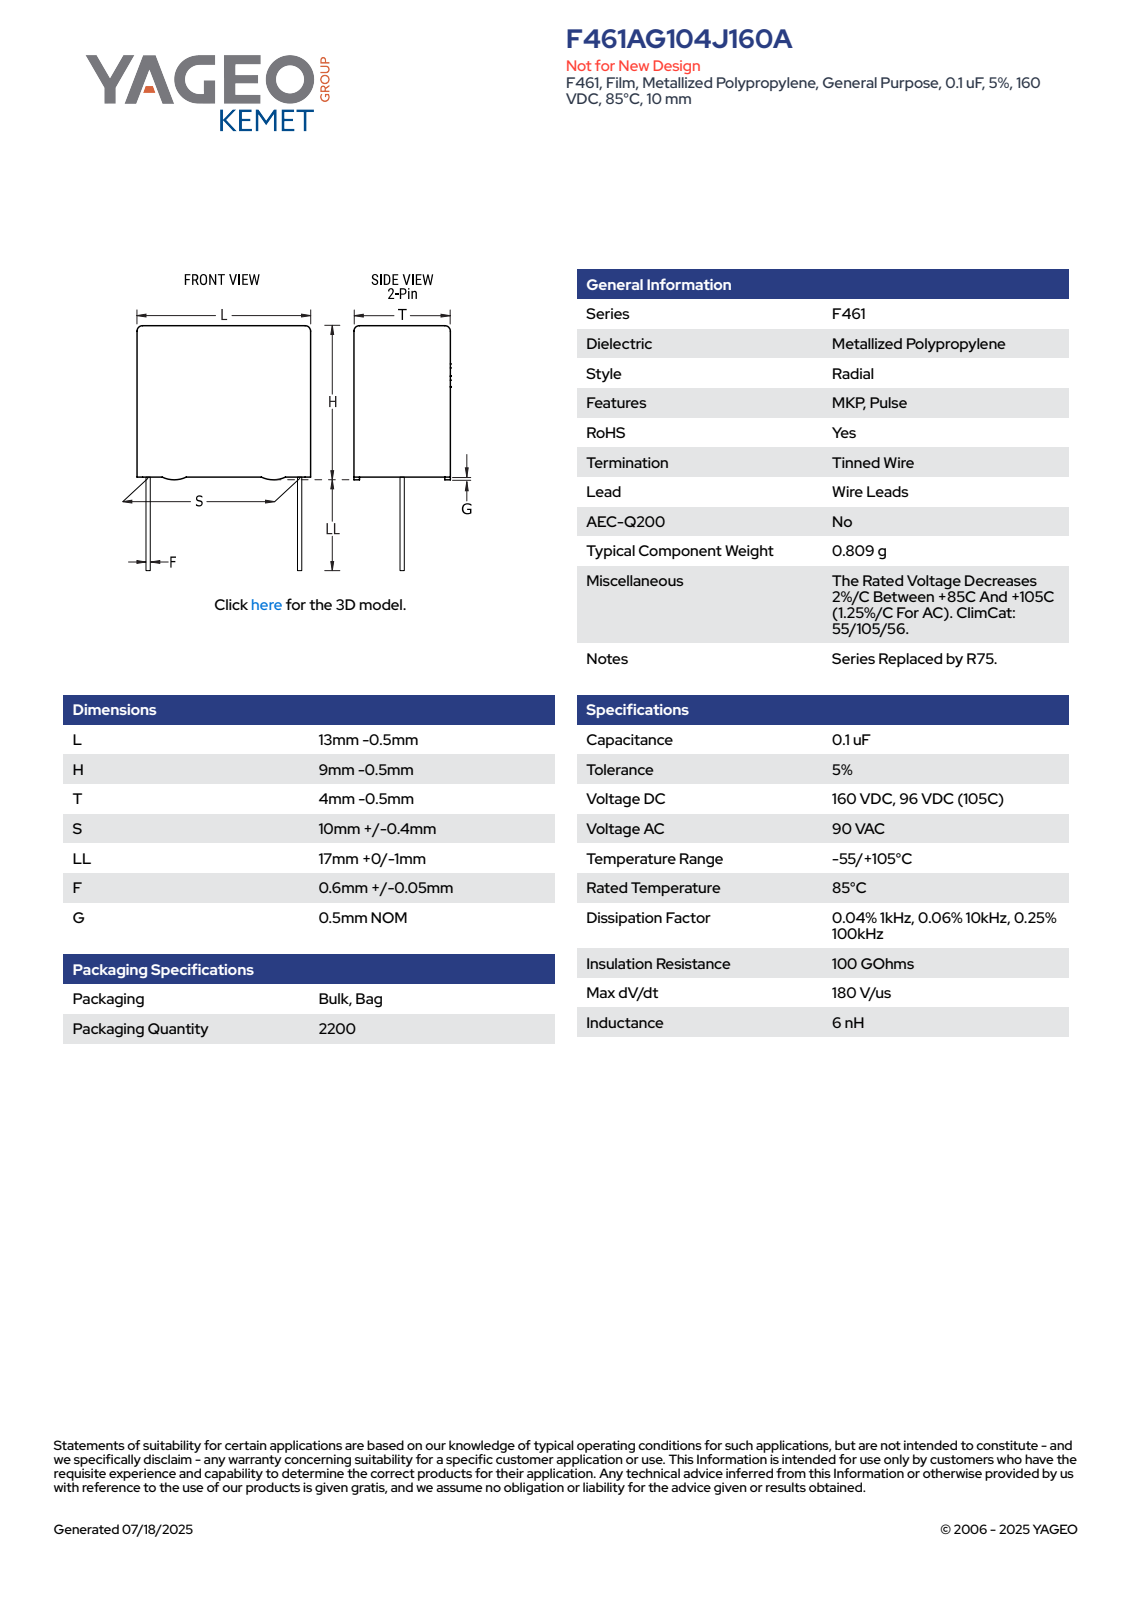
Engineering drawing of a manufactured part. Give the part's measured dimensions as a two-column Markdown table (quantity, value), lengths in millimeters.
| quantity | value |
| --- | --- |
| part name | CFR_RBG_13X9X4_L12.5H8.5T3.5S10LL17F0.65G0.5 |
| STEP written by | SolidWorks 2021 (AUTOMOTIVE_DESIGN) |
| units | millimeters |
| bodies | 4 solids, 89 faces (81 planar, 8 cylindrical, 0 other) |
| overall size | 25.5 × 12.5 × 3.5 |
| volume | 361 mm³ |
| surface area | 434 mm² |
| round bosses / shafts (diameter × count) | 0.65 × 2 |
| partial cylindrical surfaces (radius × count) | 0.5 × 4 |
| main face-to-face distances | 3.5, 8, 12.5, 3.3, 3.1, 0.5, 8.5, 17, 17.5, 25.5 |
